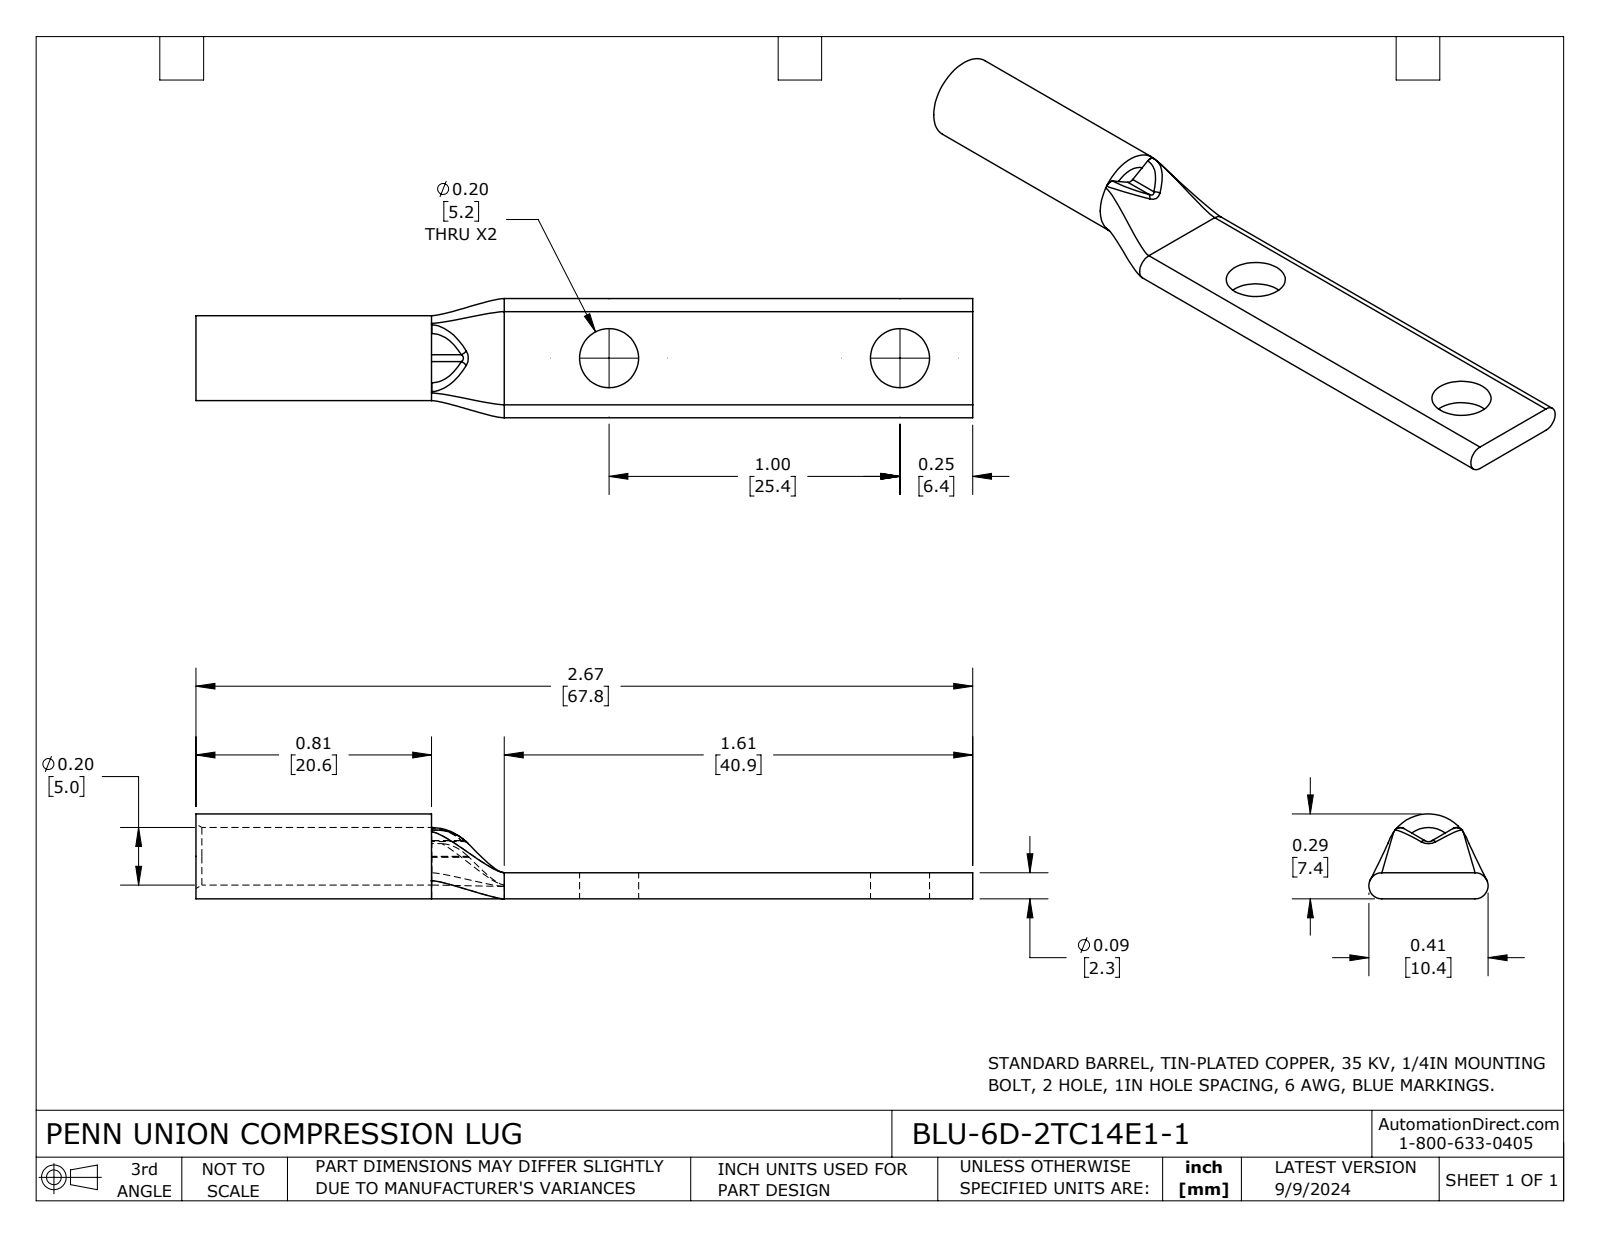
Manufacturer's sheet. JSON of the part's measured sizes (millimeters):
{"part_name": "BLU-6D-2TC14E1-1", "step_written_by": "SolidWorks 2023 (CONFIG_CONTROL_DESIGN)", "units": "millimeters", "bodies": {"solids": 1, "faces": 39, "planar": 11, "cylindrical": 13, "other": 15}, "overall_size": [67.8, 10.4, 7.4], "volume_mm3": 1400, "surface_area_mm2": 2073, "round_holes": [[5.2, 2], [5, 1]], "round_bosses_or_shafts": [[7.4, 1]], "partial_cylinders_radius": [[0.6, 2], [1.1, 2]], "face_to_face_distances": [2.3, 67.8, 20.6, 47.2, 1.2, 26.9, 6.4, 40.9], "hole_center_spacings": [25.4]}
